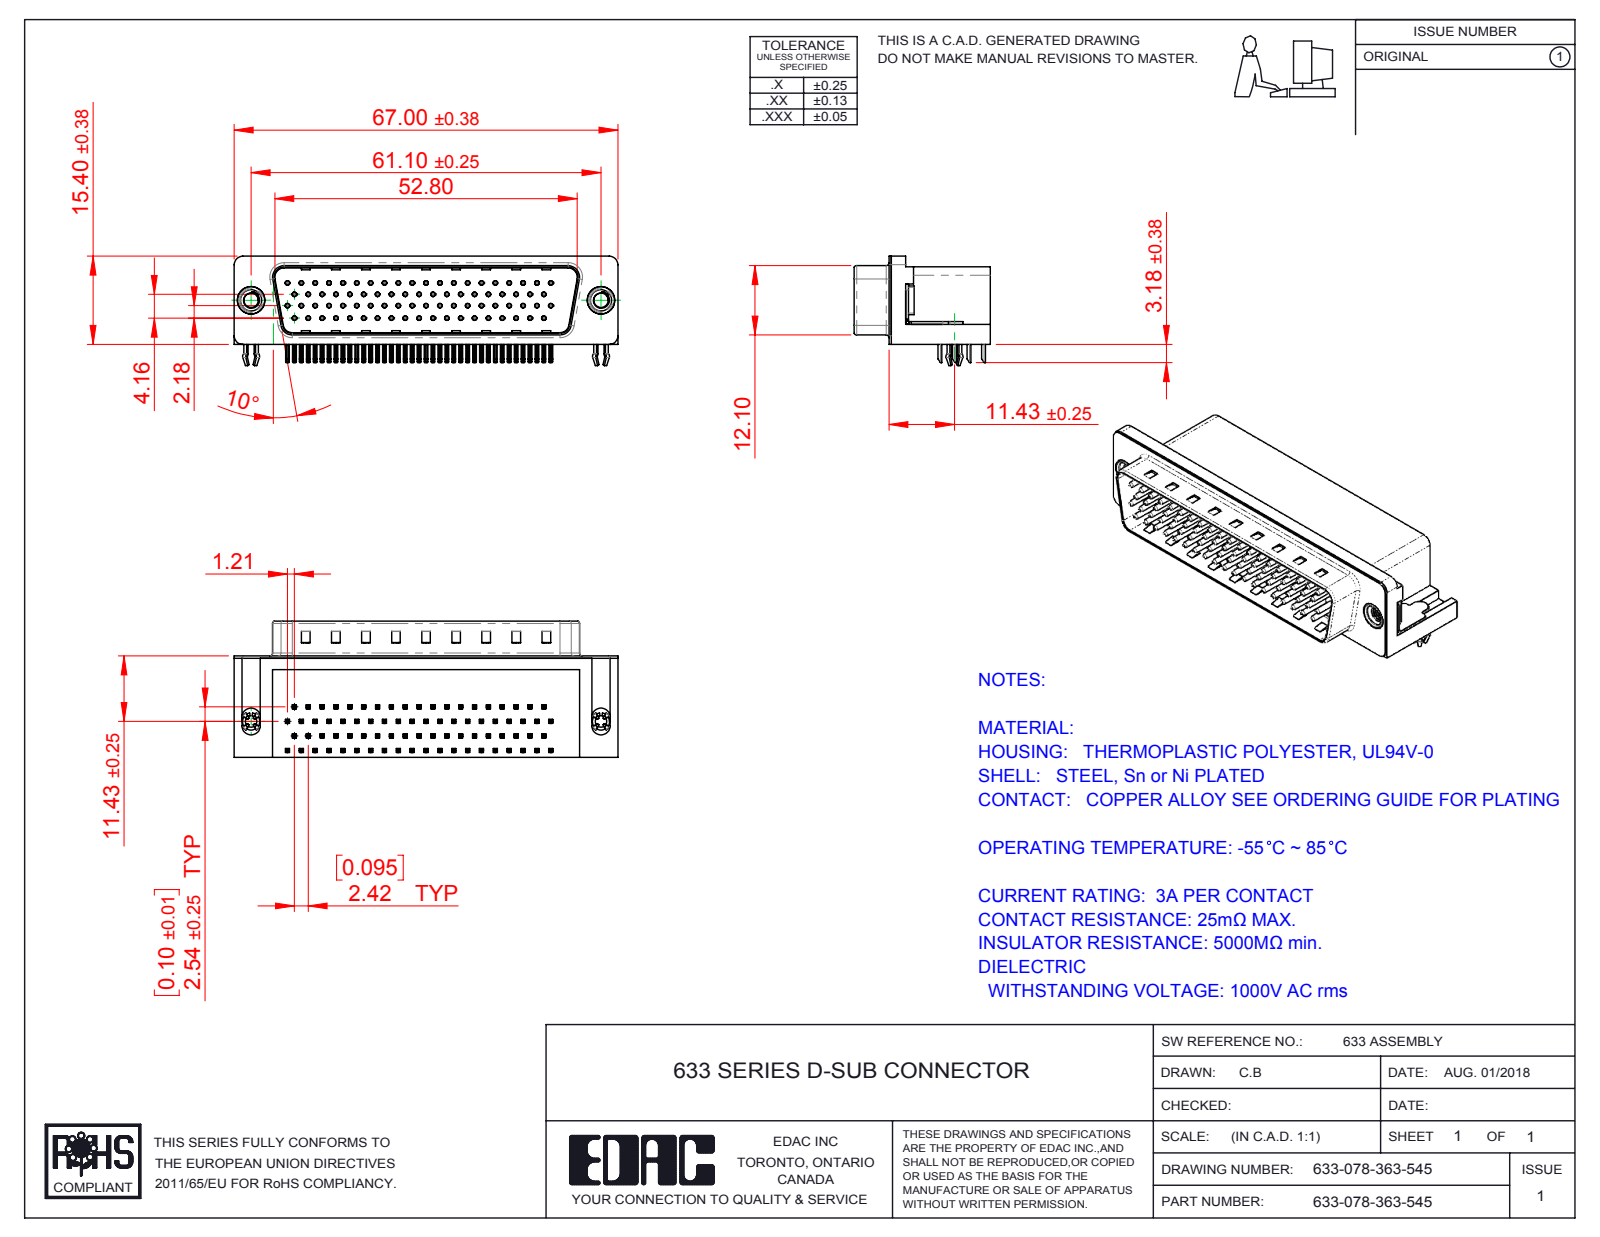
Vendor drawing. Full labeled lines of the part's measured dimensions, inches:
Part name (STEP PRODUCT): 633-078-363-545; 633 Housing_78 Contact; 633 Contact Middle_78 Contact; 633 Shell_78 Contact (+5 more)
STEP written by: SolidWorks 2016 (CONFIG_CONTROL_DESIGN)
Units: inches
Bodies: 84 solids, 6396 faces (4023 planar, 1788 cylindrical, 585 other)
Overall size (bounding box): 2.638 × 0.937 × 0.752
Volume: 0.892 in³ · Surface area: 25.47 in²
Round holes (diameter × count): ⌀0.014 ×78, ⌀0.031 ×78, ⌀0.079 ×2, ⌀0.098 ×2, ⌀0.157 ×2, ⌀0.189 ×2, ⌀0.197 ×2
Round bosses / shafts (diameter × count): ⌀0.03 ×78, ⌀0.193 ×2, ⌀0.187 ×2, ⌀0.154 ×2, ⌀0.118 ×2
Partial cylindrical surfaces — rounded edges, fillets, slot ends (radius × count): R0.01 ×324, R0.005 ×156, R0.039 ×16, R0.02 ×9, R0.063 ×8, R0.059 ×6, R0.018 ×4, R0.035 ×4
Main face-to-face distances: 0.016, 0.52, 0.681, 0.461, 0.526, 0.081, 0.541, 0.065, 0.073, 0.469
Hole centre spacings: 0.095, 0.191, 0.286, 0.381, 0.246, 0.281, 0.476, 0.339
